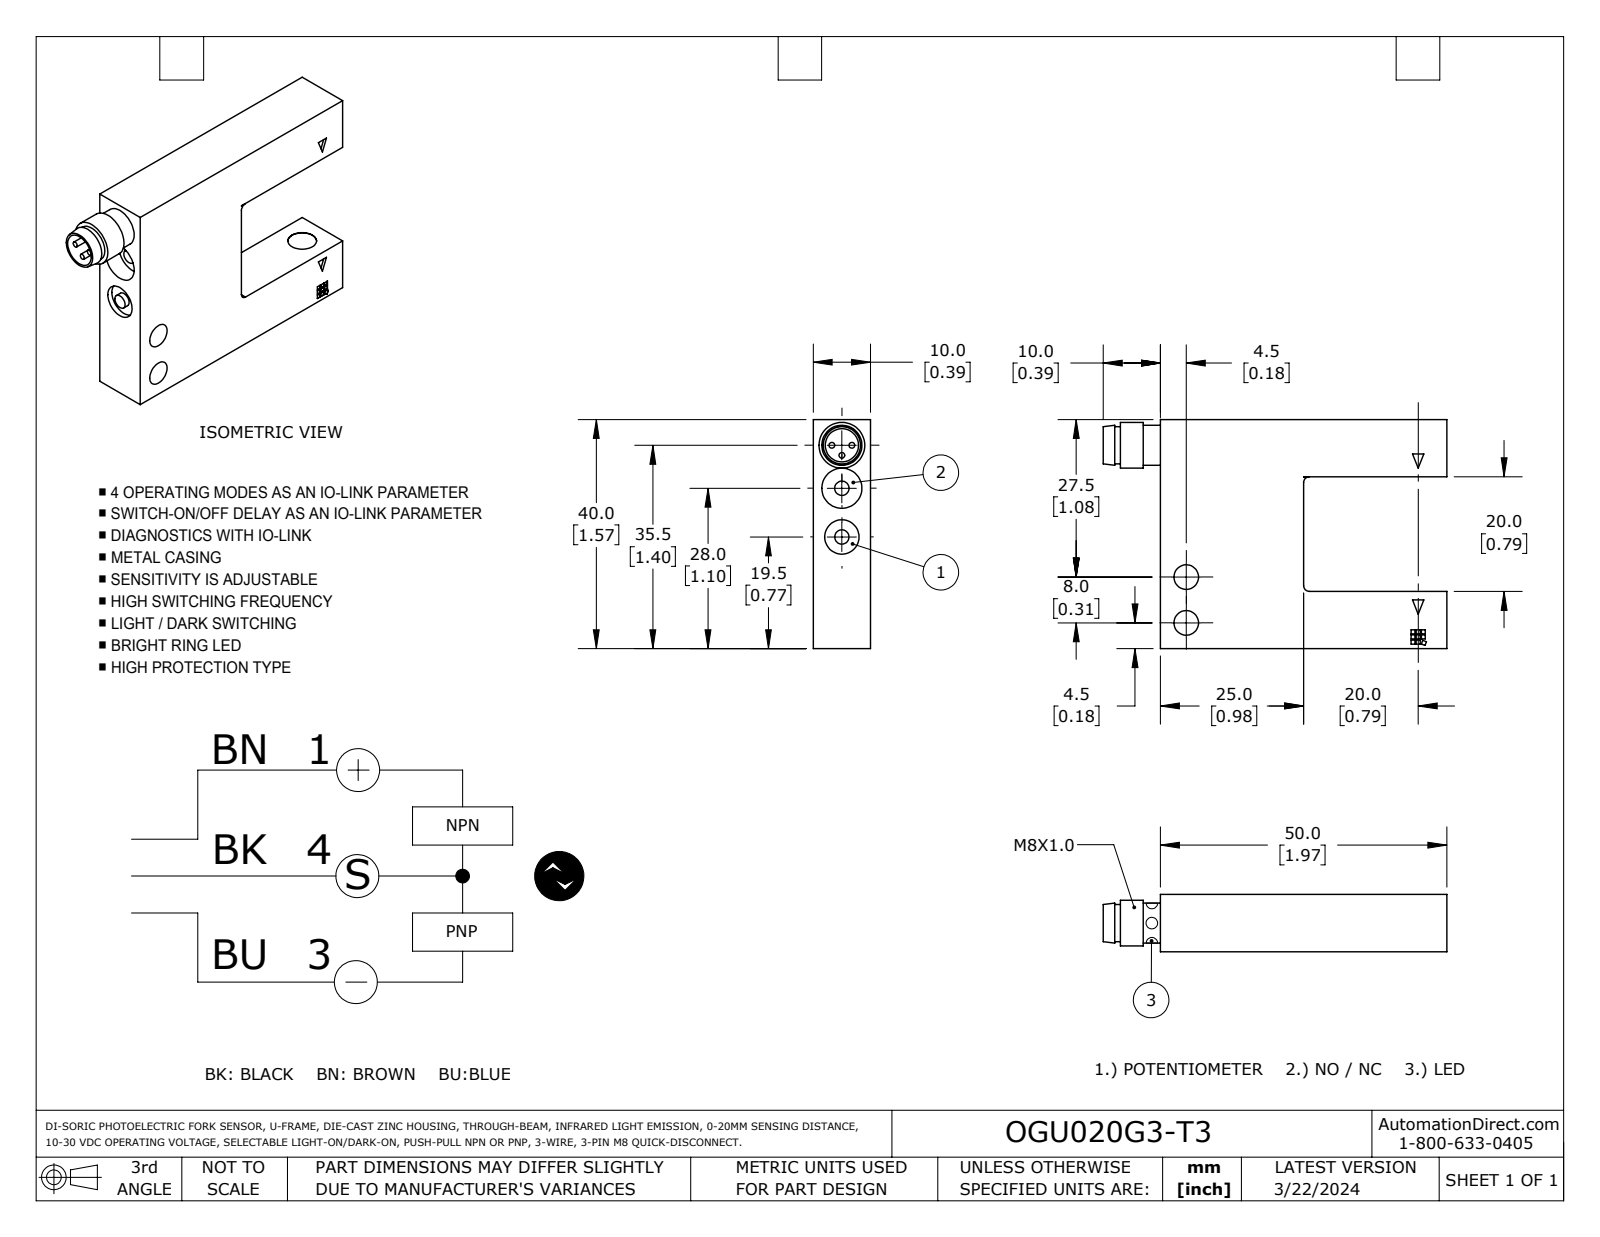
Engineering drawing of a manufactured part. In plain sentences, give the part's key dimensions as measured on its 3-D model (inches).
The part is named "OGU020G3-T3". Its 3-D file was written by "SolidWorks 2023 (AUTOMOTIVE_DESIGN)". It is 1 solid with 111 faces: 91 planar, 19 cylindrical and 1 other. Overall it measures 2.362 by 1.575 by 0.394 inches. Its volume is 0.907 cubic inches and its surface area 9.364 square inches. Round holes: 2 of diameter 0.169, 1 of diameter 0.118, 1 of diameter 0.197, 1 of diameter 0.228, 1 of diameter 0.236, 1 of diameter 0.276. Round bosses or shafts: 3 of diameter 0.039, 2 of diameter 0.098, 1 of diameter 0.315, 1 of diameter 0.276, 1 of diameter 0.256. Partial cylindrical surfaces (rounded edges, fillets, slot ends): 3 of radius 0.039. The main face-to-face distances are 0.394, 1.575, 1.181, 0.984, 0.787, 1.969, 0.392, 0.039, 1.183, 0.789. The hole center spacings are 0.295, 0.315, 0.335, 0.63.
